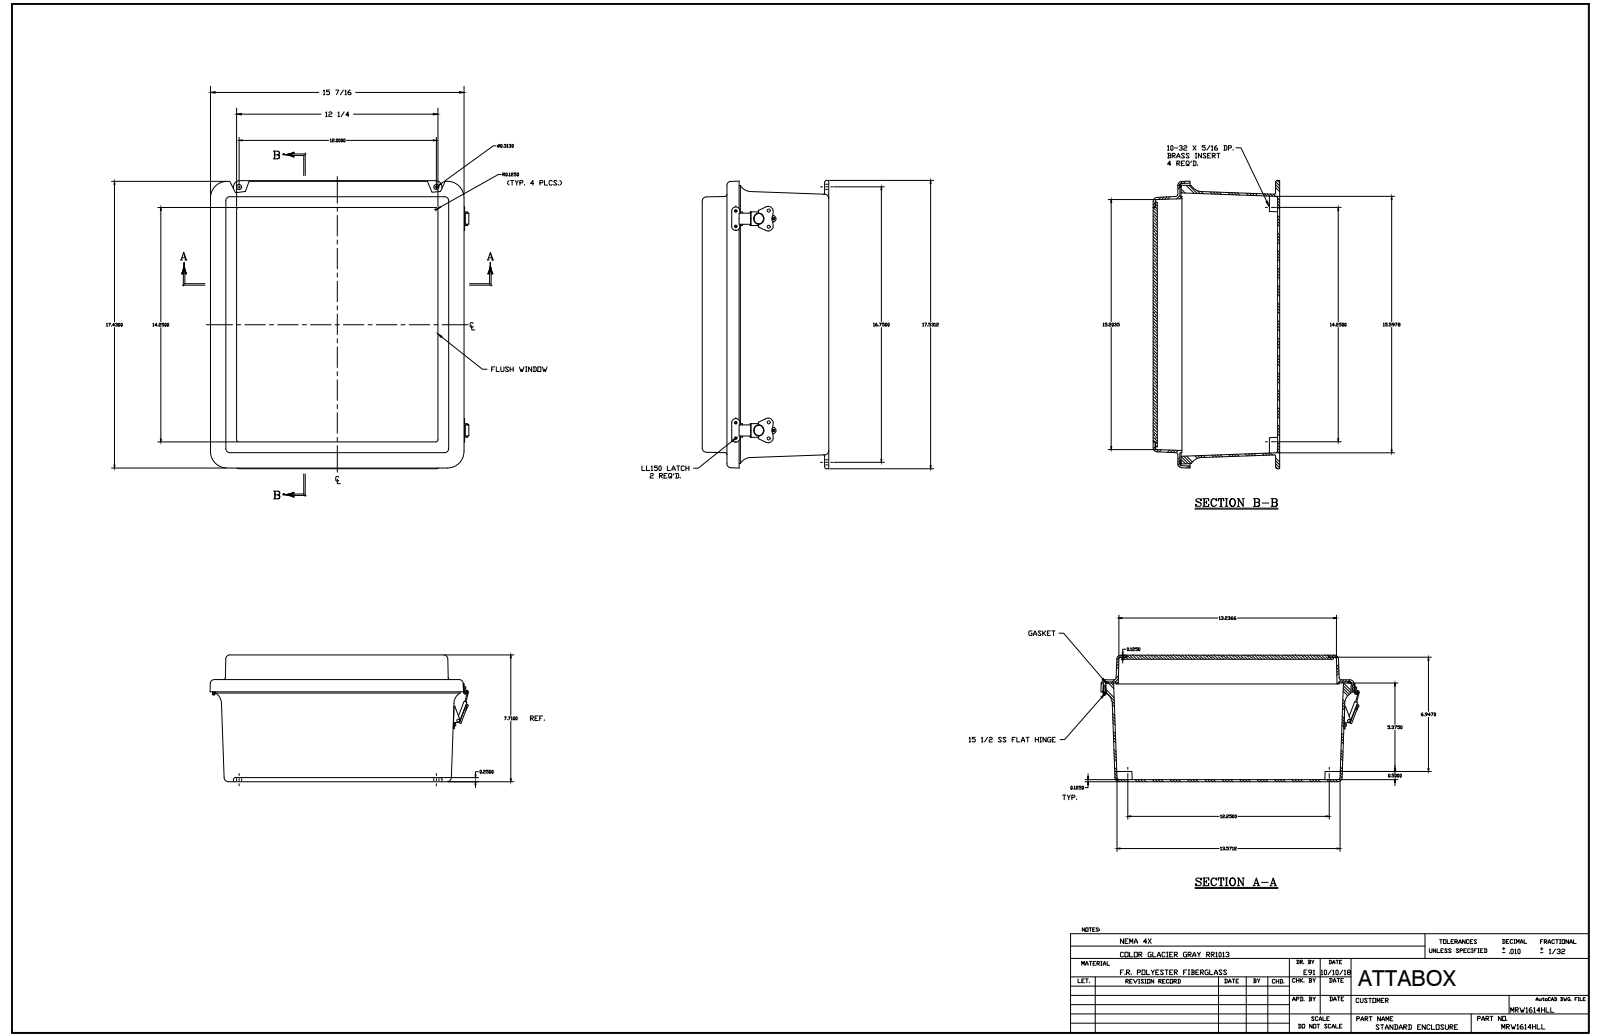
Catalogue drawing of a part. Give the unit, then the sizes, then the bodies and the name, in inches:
Units: inches
Overall size (bounding box): 17.531 × 15.625 × 7.697
Round holes (diameter × count): ⌀0.14 ×18, ⌀0.131 ×10, ⌀0.152 ×8, ⌀0.13 ×4, ⌀0.156 ×4, ⌀0.165 ×4, ⌀0.197 ×4, ⌀0.218 ×4, ⌀0.118 ×2, ⌀0.138 ×2, ⌀0.181 ×2, ⌀0.182 ×2
Round bosses / shafts (diameter × count): ⌀0.25 ×18, ⌀0.125 ×11, ⌀0.125 ×7, ⌀0.27 ×4, ⌀0.583 ×2, ⌀0.524 ×2, ⌀0.209 ×2, ⌀0.185 ×2
Partial cylindrical surfaces — rounded edges, fillets, slot ends (radius × count): R0.125 ×24, R0.031 ×20, R0.25 ×20, R0.079 ×19, R0.037 ×8, R0.039 ×8, R0.045 ×8, R0.047 ×8
Main face-to-face distances: 0.125, 7.447, 0.125, 0.25, 7.697, 7.572, 7.322, 5.945, 1.502, 6.07
Hole centre spacings: 3.75, 7.5, 12.868, 11.25, 12.869, 0.25, 3.5, 0.938
Volume: 171.3 in³ · Surface area: 2 185 in²
Bodies: 51 solids, 1342 faces (605 planar, 520 cylindrical, 217 other)
Part name (STEP PRODUCT): MRW1614HLL
STEP written by: SolidWorks 2018 (AUTOMOTIVE_DESIGN)
